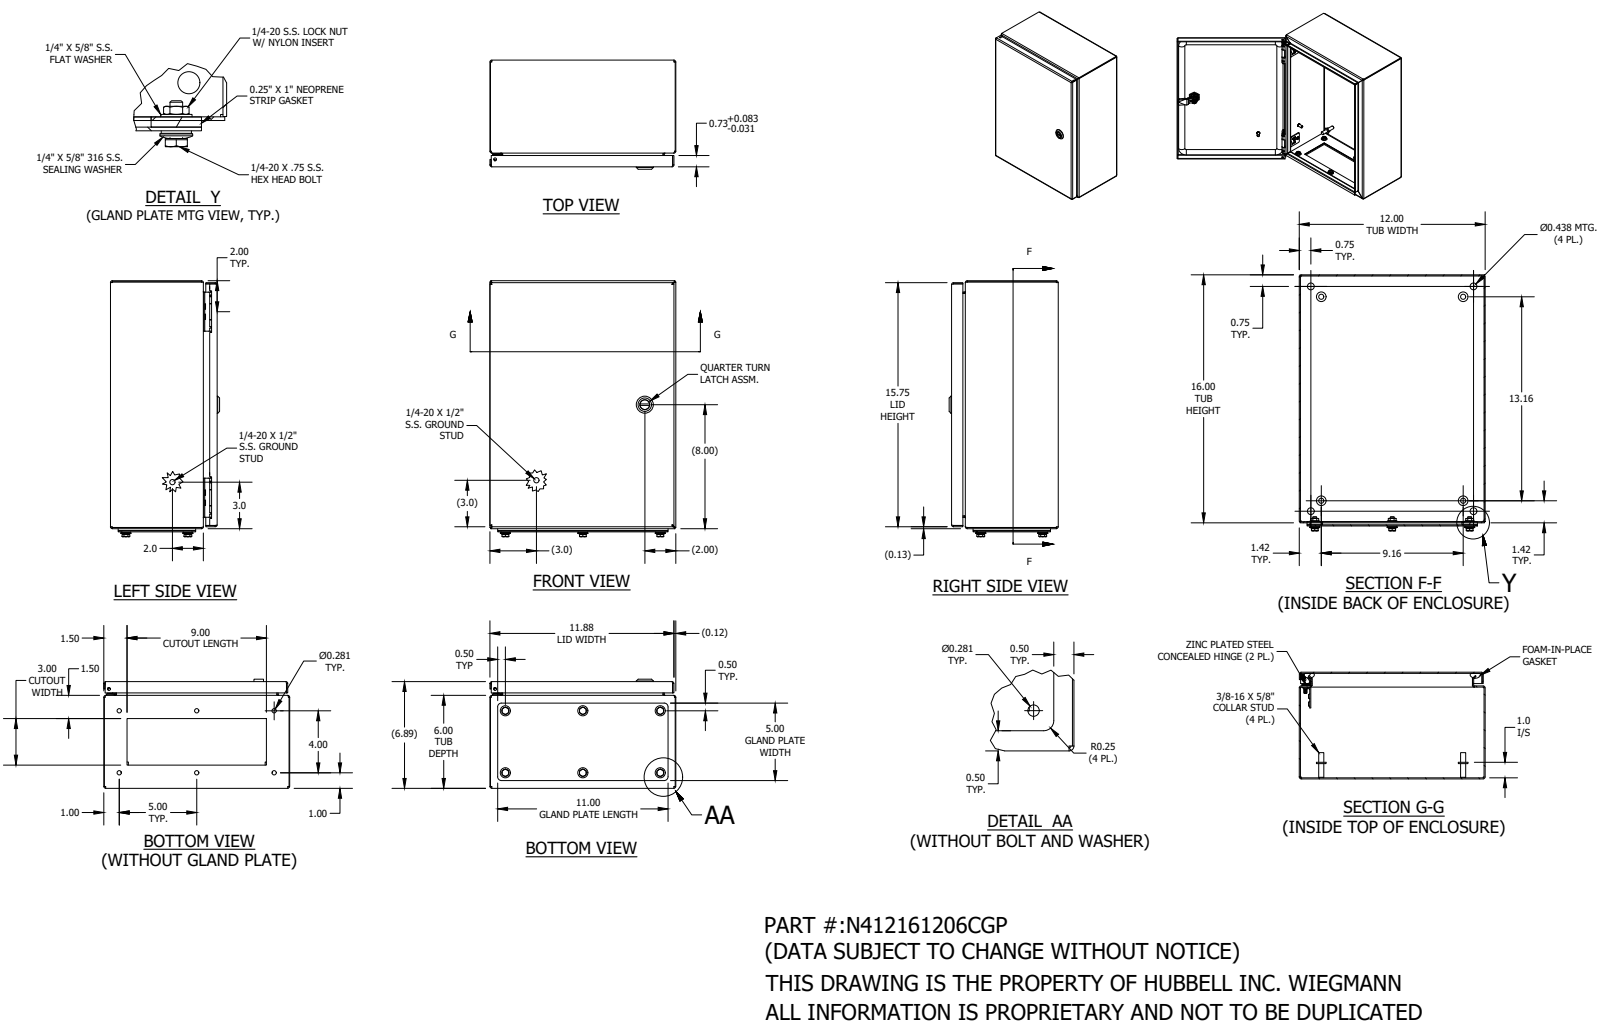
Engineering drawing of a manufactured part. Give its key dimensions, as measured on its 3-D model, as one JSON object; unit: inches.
{"part_name": "N412161206CGP", "step_written_by": "SolidWorks 2019 (AUTOMOTIVE_DESIGN)", "units": "inches", "bodies": {"solids": 63, "faces": 1909, "planar": 740, "cylindrical": 600, "other": 569}, "overall_size": [16.519, 12, 7.044], "volume_in3": 79.37, "surface_area_in2": 1930, "round_holes": [[0.281, 12], [0.16, 8], [0.211, 6], [0.29, 6], [0.35, 6], [0.188, 5], [0.093, 4], [0.167, 4], [0.275, 4], [0.437, 4], [0.235, 3], [0.235, 3]], "round_bosses_or_shafts": [[0.25, 16], [0.625, 9], [0.65, 6], [0.6, 6], [0.438, 6], [0.36, 4], [0.33, 4], [0.32, 4]], "partial_cylinders_radius": [[0.012, 30], [0.05, 26], [0.047, 20], [0.121, 20], [0.02, 13], [0.125, 8], [0.13, 8], [0.157, 5]], "face_to_face_distances": [0.074, 6.812, 6.738, 6.886, 0.074, 16.13, 11.926, 11.926, 11.852, 12], "hole_center_spacings": [4, 5, 6.403, 0.66, 12.004, 5, 5, 6.403]}
